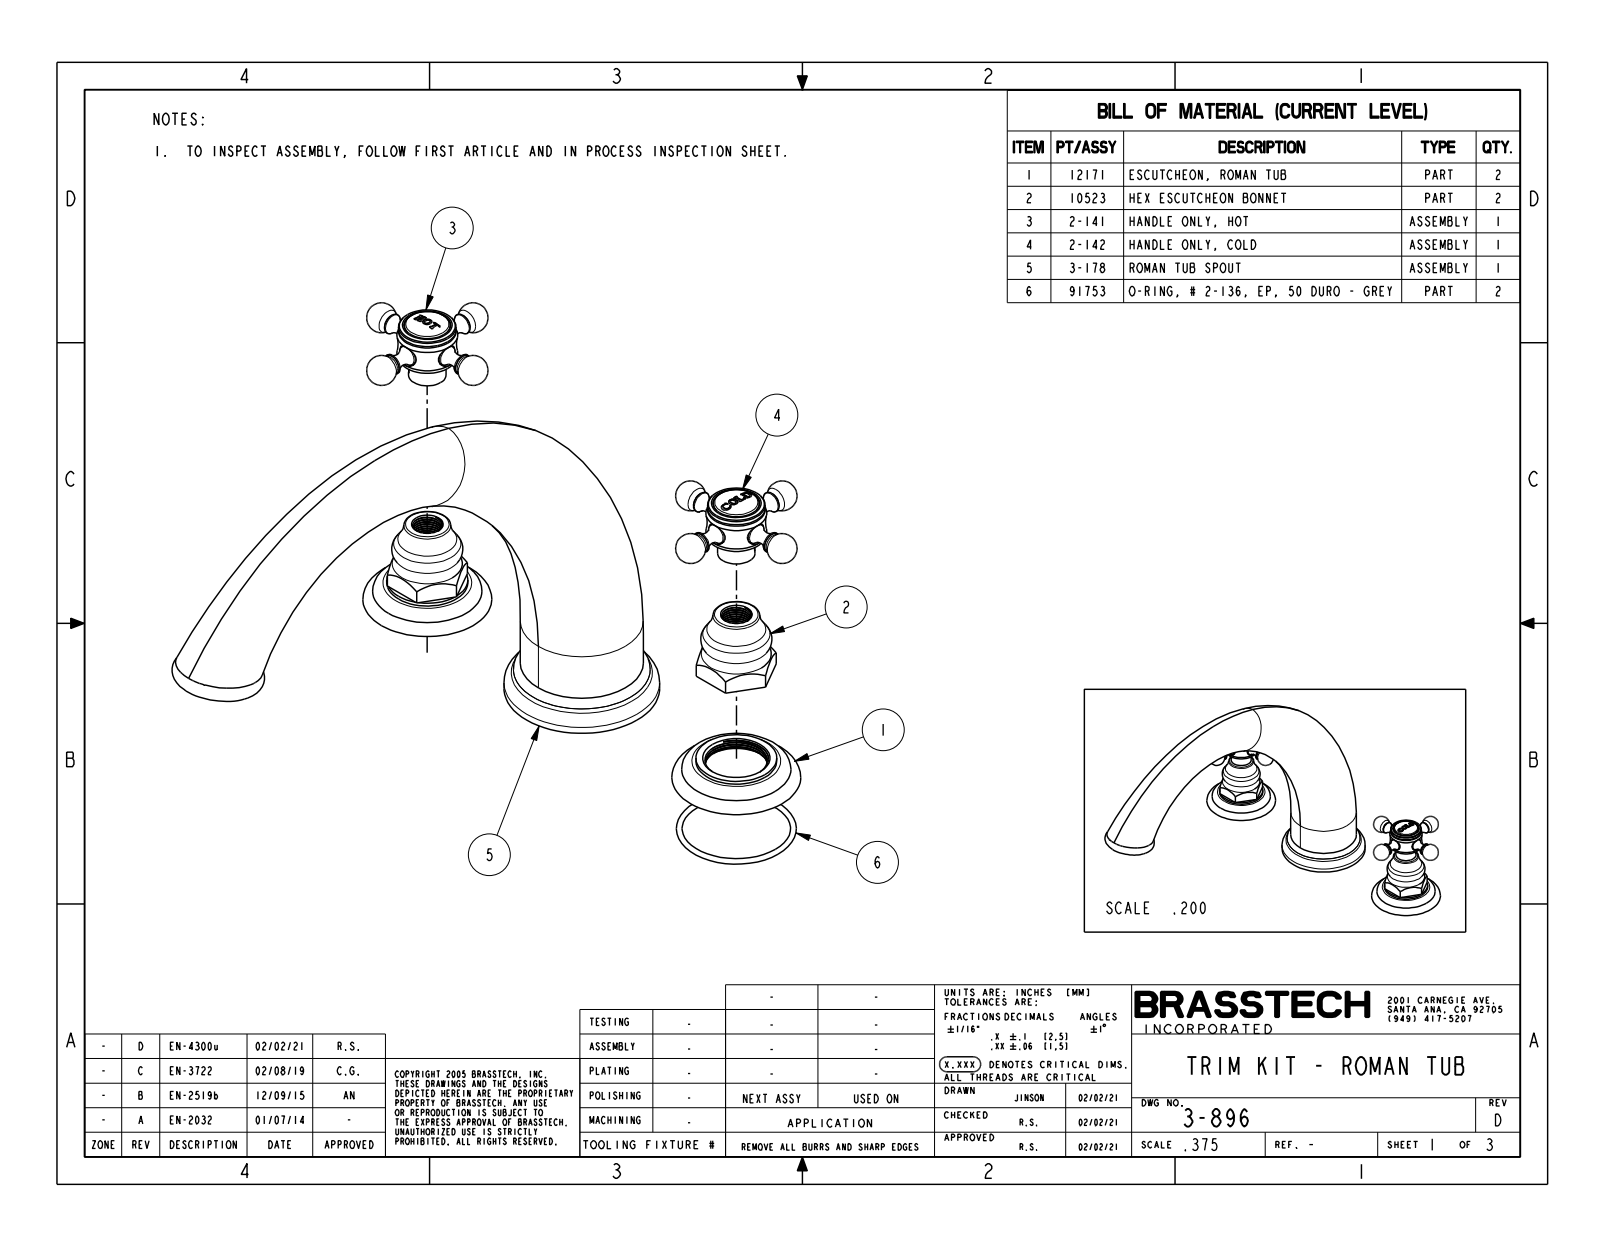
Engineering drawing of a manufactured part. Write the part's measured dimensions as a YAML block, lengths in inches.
part_name: "3-896"
step_written_by: "CREO PARAMETRIC BY PTC INC, 2018400 (CONFIG_CONTROL_DESIGN)"
units: inches
bodies: {solids: 3, faces: 427, planar: 125, cylindrical: 96, other: 206}
overall_size: [11.713, 10.915, 7.801]
volume: 44.53
surface_area: 140.1
round_holes:
  - {diameter: 0.41, count: 3}
  - {diameter: 0.855, count: 2}
round_bosses_or_shafts:
  - {diameter: 0.392, count: 3}
  - {diameter: 1.482, count: 2}
  - {diameter: 1.055, count: 2}
  - {diameter: 0.687, count: 2}
  - {diameter: 0.4, count: 2}
  - {diameter: 2.85, count: 1}
  - {diameter: 2.506, count: 1}
partial_cylinders:
  - {radius: 0.006, count: 7}
  - {radius: 0.024, count: 7}
  - {radius: 0.03, count: 5}
  - {radius: 0.048, count: 3}
  - {radius: 0.018, count: 2}
  - {radius: 0.036, count: 2}
  - {radius: 0.041, count: 2}
  - {radius: 0.054, count: 1}
face_to_face_distances: [6.928, 1.313, 1.687, 0.375, 1.312, 1.718, 1.343, 0.031, 1.313, 8.241]
hole_center_spacings: [8]
